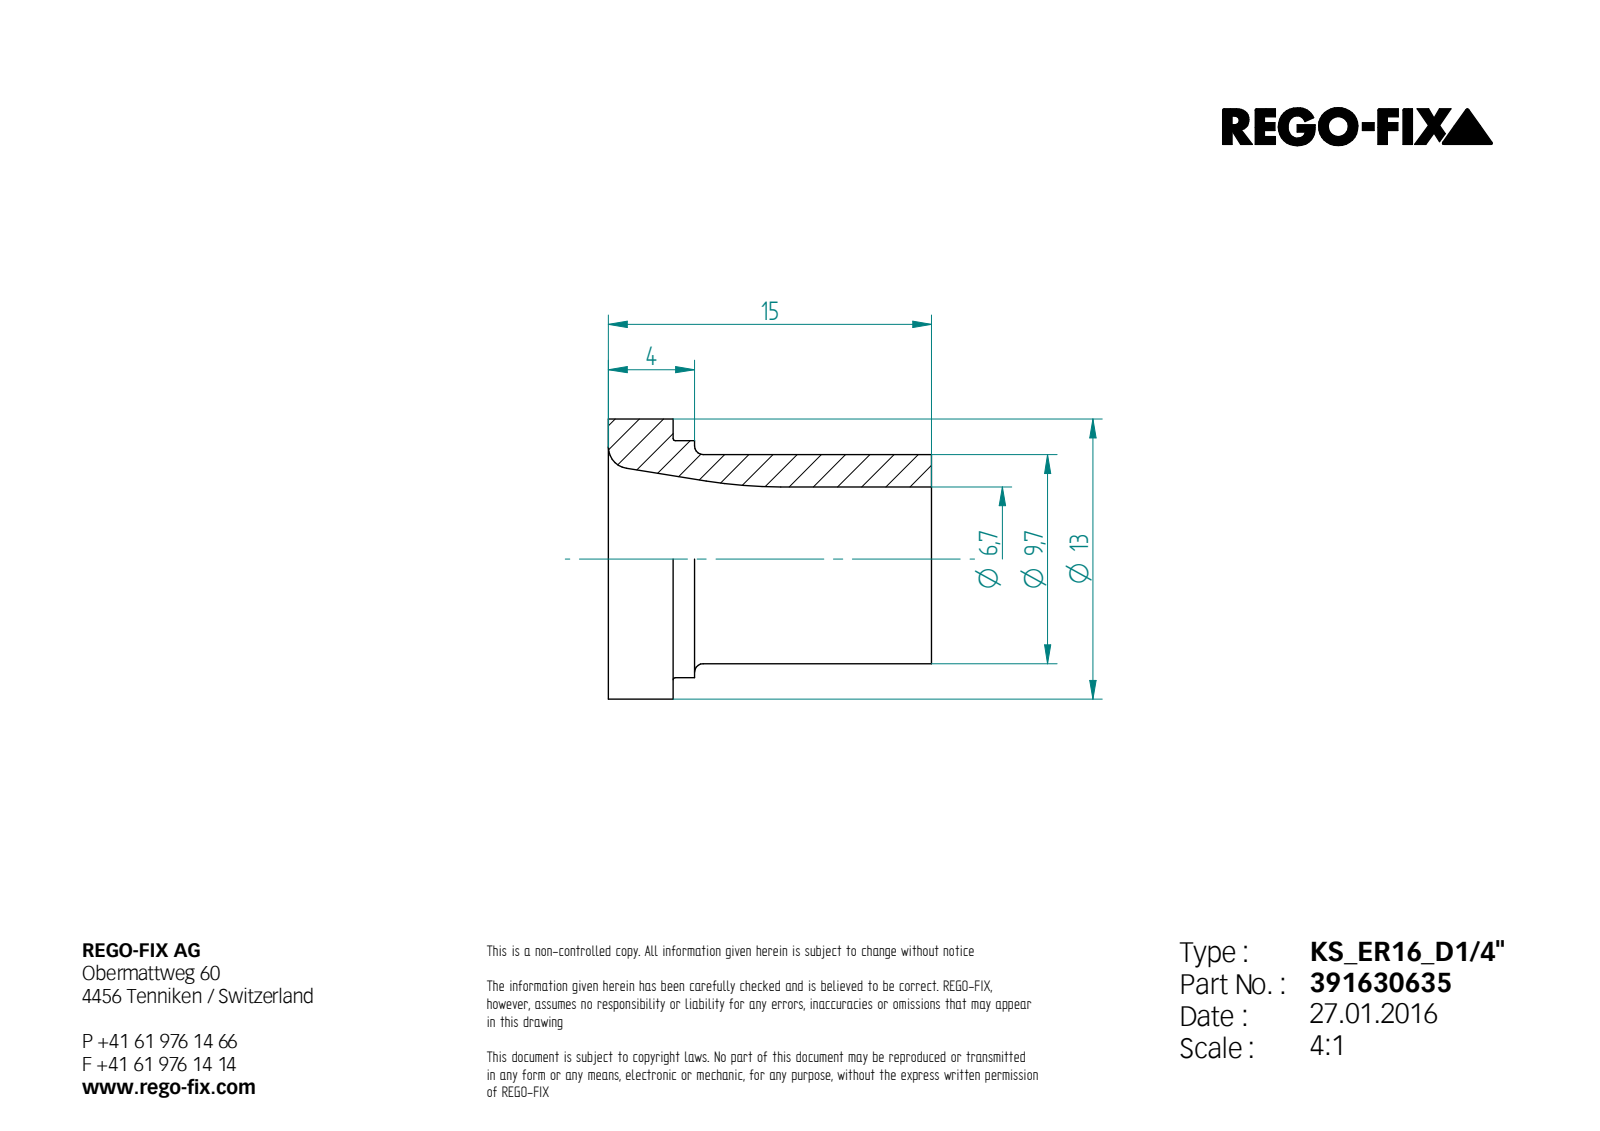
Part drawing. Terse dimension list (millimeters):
written by: Unknown (AUTOMOTIVE_DESIGN)
unit: mm
bodies: 1 solid, 13 faces (4 planar, 4 cylindrical, 5 other)
size: 15 × 13 × 13
volume: 700 mm³; area: 986 mm²
holes: 1× ⌀6.7
bosses: 1× ⌀13, 1× ⌀11, 1× ⌀9.7
face distances: 15, 3, 12, 4, 1, 11
